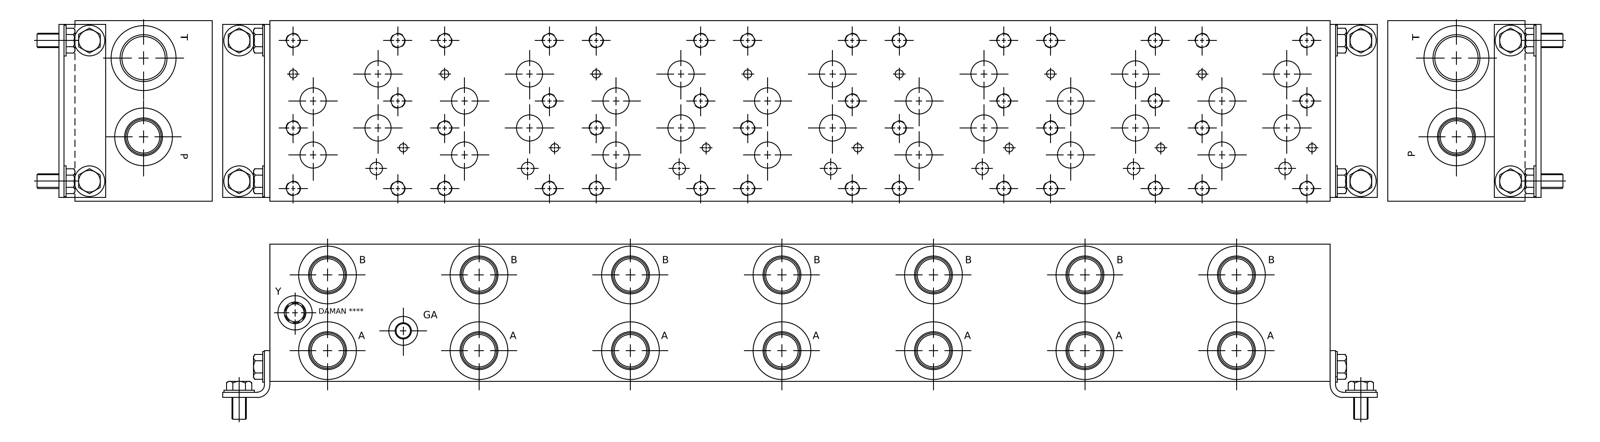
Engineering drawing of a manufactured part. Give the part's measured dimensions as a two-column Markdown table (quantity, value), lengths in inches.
| quantity | value |
| --- | --- |
| part name | Part_AD08P075S_3D |
| STEP written by | Autodesk Inventor 2020 (AUTOMOTIVE_DESIGN) |
| units | inches |
| bodies | 1 solid, 1227 faces (545 planar, 255 cylindrical, 427 other) |
| overall size | 36.75 × 6.25 × 4.75 |
| volume | 1 036 in³ |
| surface area | 1 107 in² |
| round holes (diameter × count) | 0.422 × 45, 0.5 × 44, 0.906 × 27, 1.231 × 15, 1.329 × 15, 1.934 × 15, 0.281 × 14, 1.125 × 14, 1.313 × 14, 1.398 × 14, 0.438 × 6, 1.313 × 2 |
| main face-to-face distances | 4.75, 6.25, 0.031, 36.75, 6.219, 36.719, 36.688, 0.781, 0.75, 3.56 |
| hole center spacings | 5.25, 10.5, 15.75, 21, 7.558, 10.666, 5.87, 8.303 |
